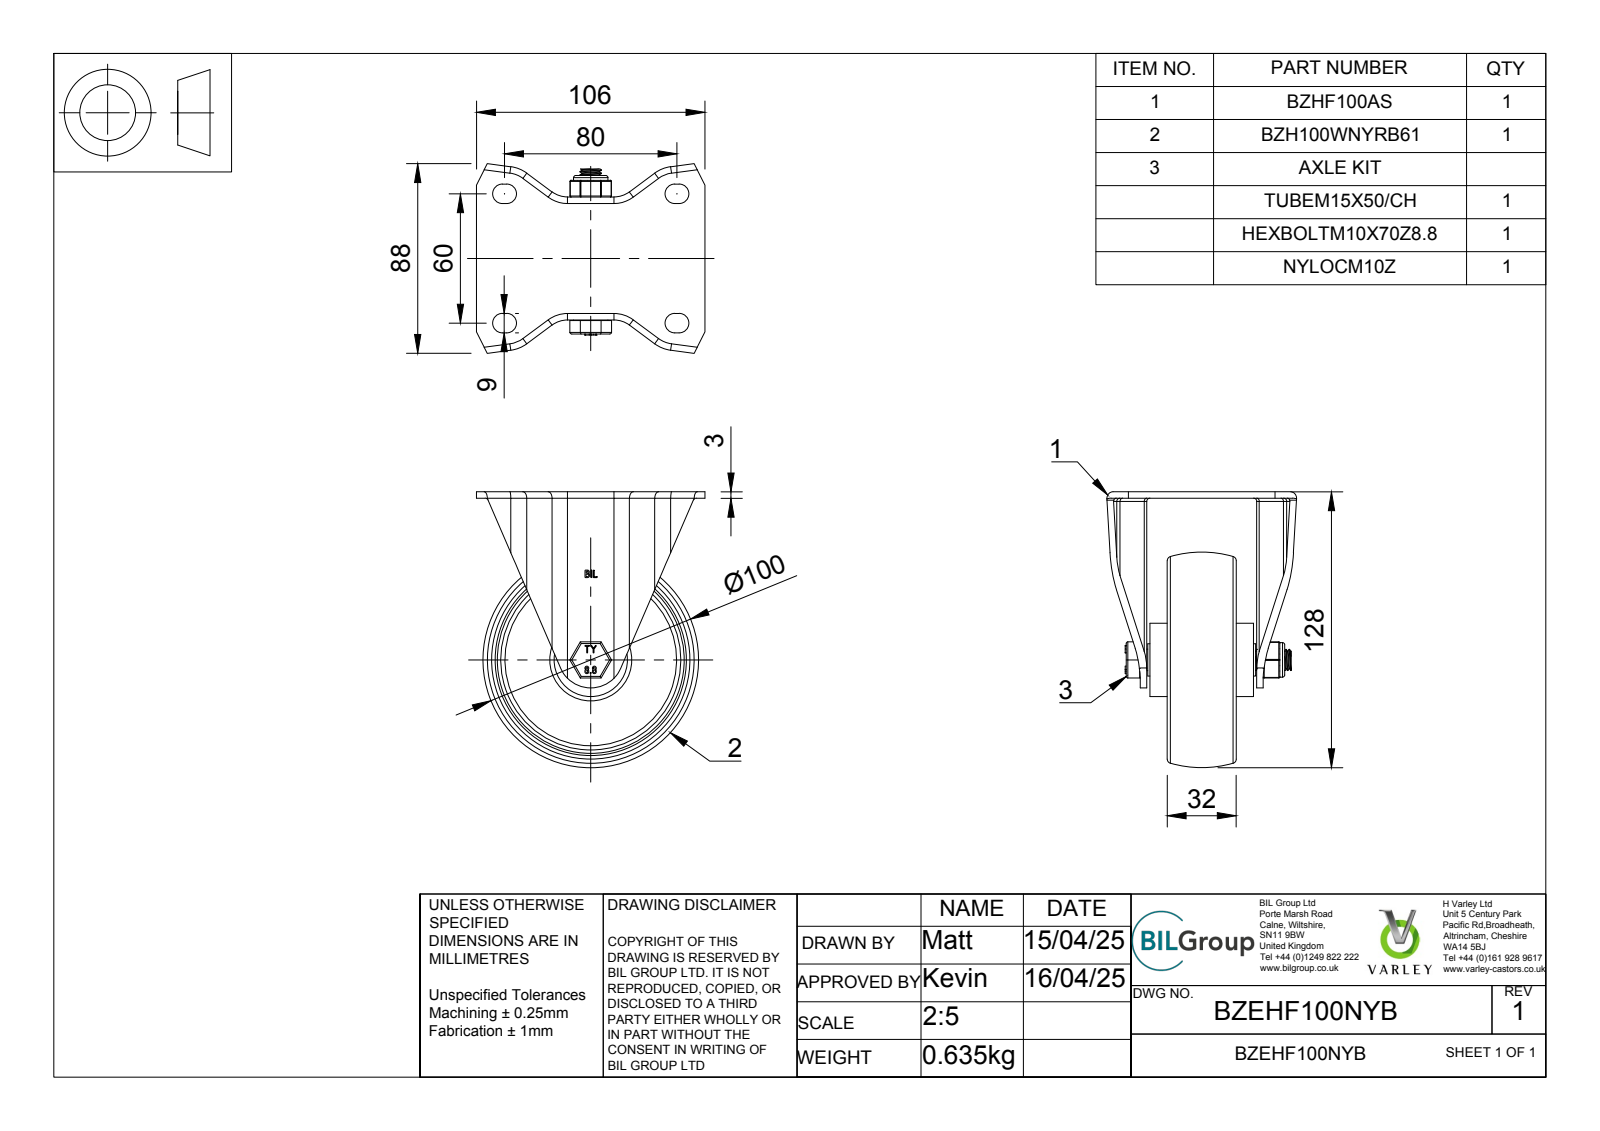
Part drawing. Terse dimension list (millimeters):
name: BZEHF100NYB v3; BZHF100AS v1; ZINC PLATED, PRESSED STEEL BRACKET; BZH100WNYRB61 v1 (+7 more)
written by: Autodesk Translation Framework v14.4.0.0 (AUTOMOTIVE_DESIGN)
unit: mm
bodies: 17 solids, 453 faces (204 planar, 159 cylindrical, 90 other)
size: 128 × 106 × 88
volume: 199 522 mm³; area: 93 935 mm²
holes: 1× ⌀10, 1× ⌀10.25, 1× ⌀10.5, 1× ⌀12, 1× ⌀15, 1× ⌀15.2
bosses: 8× ⌀4, 1× ⌀34, 1× ⌀23, 1× ⌀22.75, 1× ⌀16, 1× ⌀9.85, 1× ⌀8.14
rounds: 18× R0.5, 12× R1.5, 10× R3, 8× R4.5, 6× R0.75, 4× R6, 4× R8, 4× R12
face distances: 3, 8, 21.5, 29.5, 54, 24.5, 32.5, 3.01, 25.27, 51
